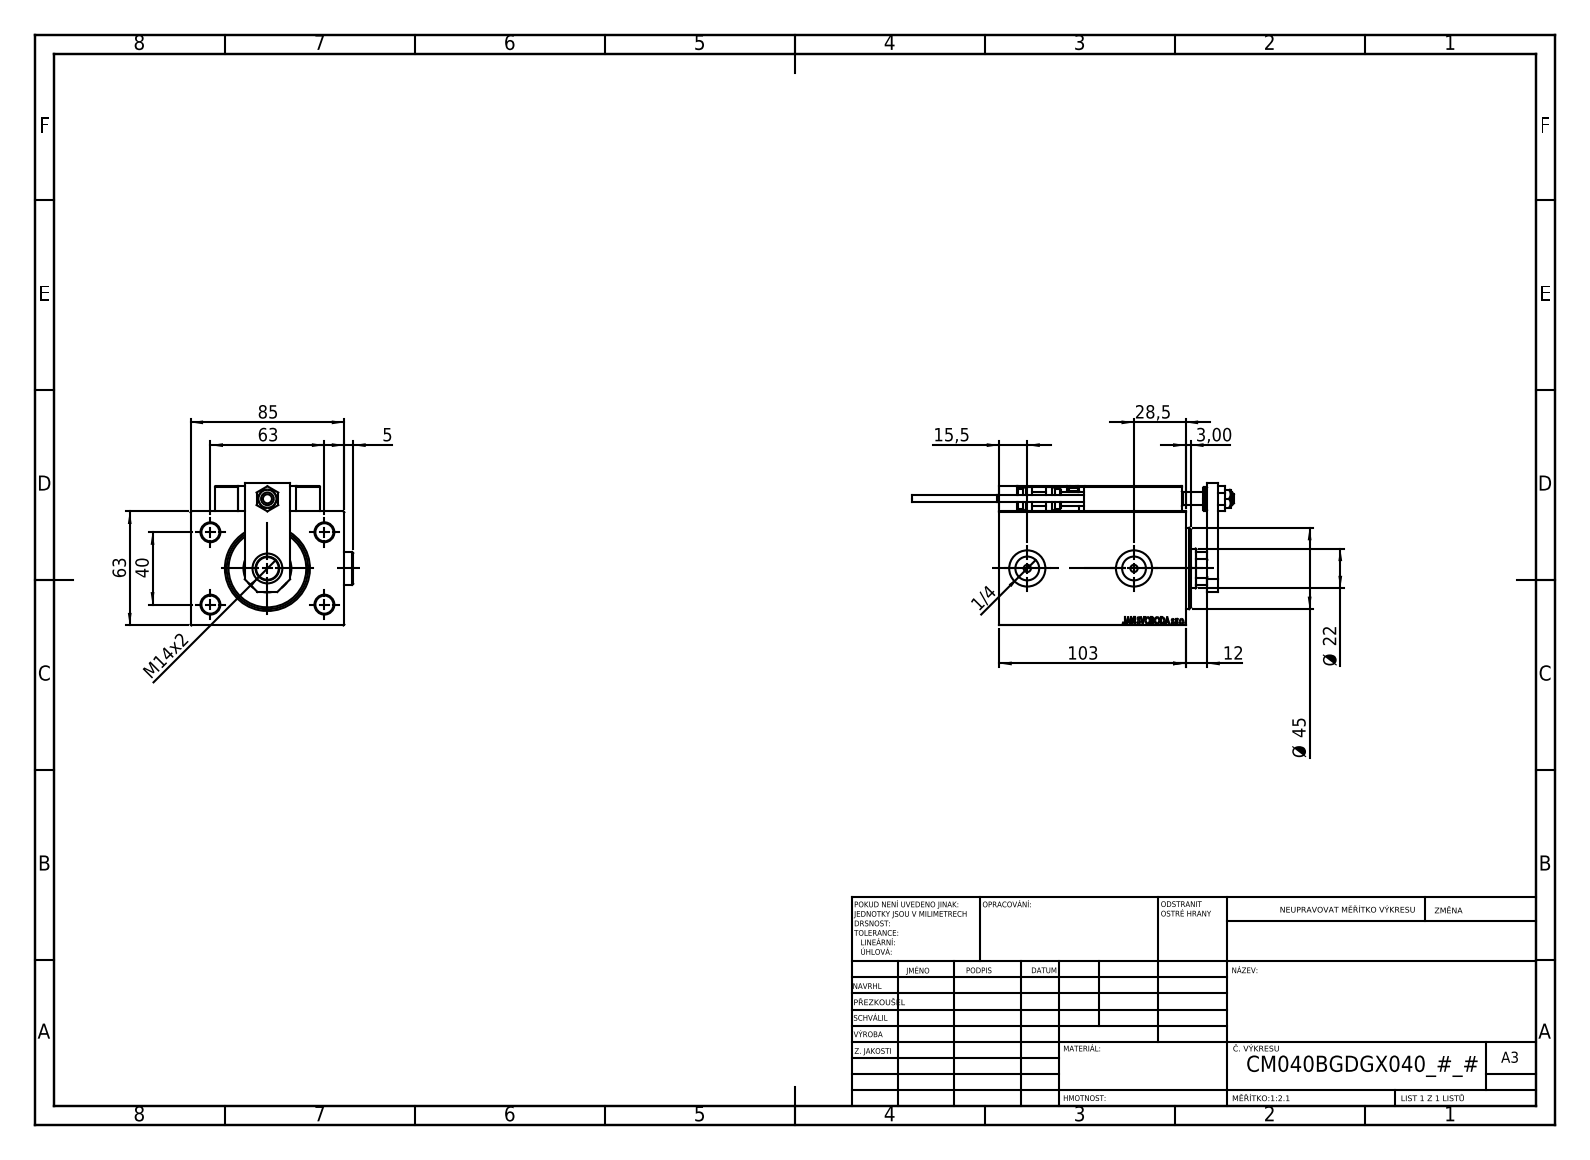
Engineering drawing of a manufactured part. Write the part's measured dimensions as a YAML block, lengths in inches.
part_name: "NUT_D12; V450CM_B_Body; SWITCH DIM B,W; Block (+8 more)"
step_written_by: "SolidWorks 2019 (CONFIG_CONTROL_DESIGN)"
units: inches
bodies: {solids: 26, faces: 1372, planar: 595, cylindrical: 200, other: 577}
overall_size: [6.996, 3.539, 3.091]
volume: 33.71
surface_area: 163.2
round_holes:
  - {diameter: 0.157, count: 6}
  - {diameter: 0.315, count: 5}
  - {diameter: 0.126, count: 4}
  - {diameter: 0.394, count: 4}
  - {diameter: 0.197, count: 2}
  - {diameter: 0.518, count: 2}
  - {diameter: 0.787, count: 2}
  - {diameter: 0.276, count: 1}
  - {diameter: 0.492, count: 1}
  - {diameter: 0.65, count: 1}
  - {diameter: 0.866, count: 1}
  - {diameter: 1.004, count: 1}
round_bosses_or_shafts:
  - {diameter: 0.709, count: 2}
  - {diameter: 0.197, count: 2}
  - {diameter: 0.15, count: 2}
  - {diameter: 0.512, count: 1}
  - {diameter: 0.433, count: 1}
partial_cylinders:
  - {radius: 0.012, count: 30}
  - {radius: 0.118, count: 2}
  - {radius: 0.413, count: 1}
face_to_face_distances: [2.48, 0.472, 3.346, 4.055, 3.583, 0.551, 3.031, 0.709, 0.118, 1.181]
hole_center_spacings: [1.469, 0.448, 0.787, 1.165, 1.169, 1.42, 1.438, 1.575]
